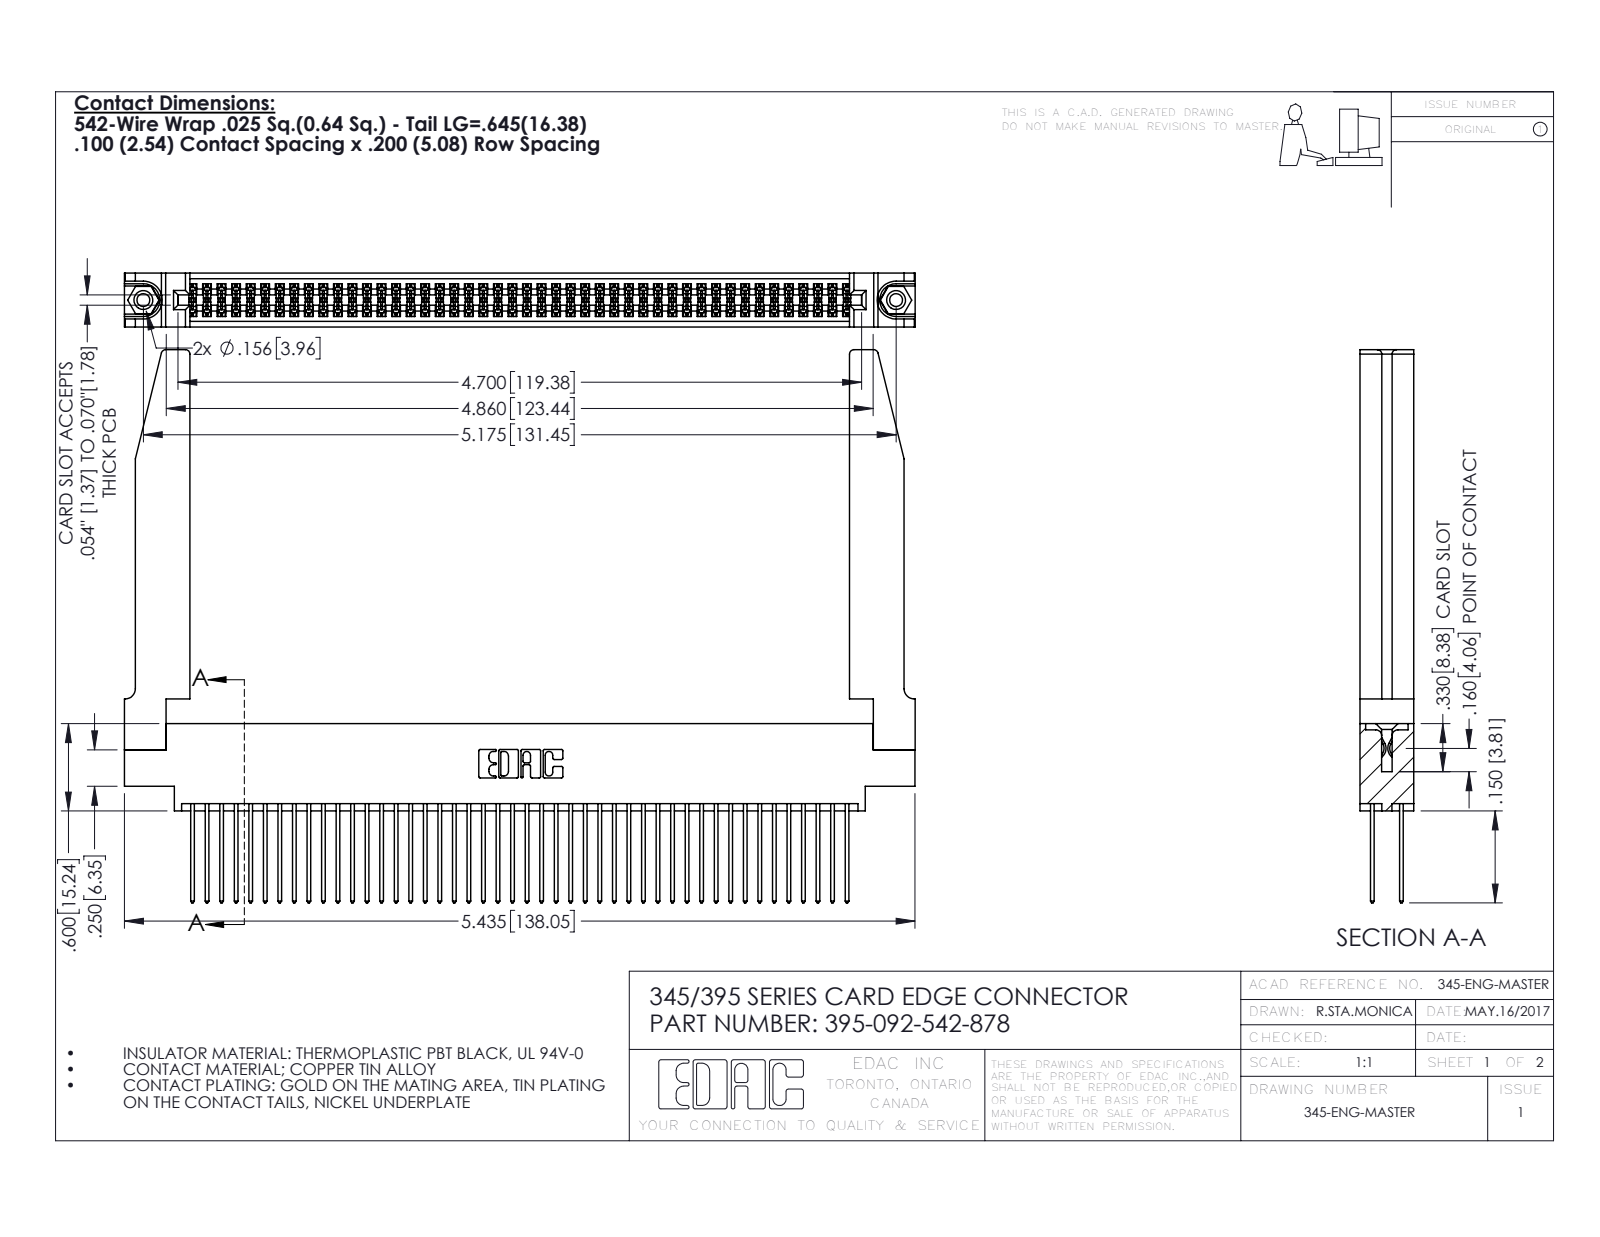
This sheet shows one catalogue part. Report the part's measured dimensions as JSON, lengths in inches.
{"part_name": "345 Part_0.170 Offset - 0.156 Dia-TH; 395-092-542-878; 345-220-078_345-220-078; 345-250-001_345-250-001-102 (+1 more)", "step_written_by": "SolidWorks 2016 (CONFIG_CONTROL_DESIGN)", "units": "inches", "bodies": {"solids": 97, "faces": 4964, "planar": 3262, "cylindrical": 1650, "other": 52}, "overall_size": [5.436, 3.802, 0.37], "volume_in3": 1.314, "surface_area_in2": 45.59, "round_holes": [[0.089, 2], [0.125, 2], [0.156, 2], [0.064, 1]], "round_bosses_or_shafts": [[0.155, 2]], "partial_cylinders_radius": [[0.006, 138], [0.01, 92], [0.01, 22], [0.03, 8], [0.007, 6], [0.031, 6], [0.026, 3], [0.014, 2]], "face_to_face_distances": [0.072, 0.298, 0.37, 0.2, 0.098, 0.272, 0.025, 0.225, 0.175, 0.148], "hole_center_spacings": [0.27, 4.939, 5.175]}
